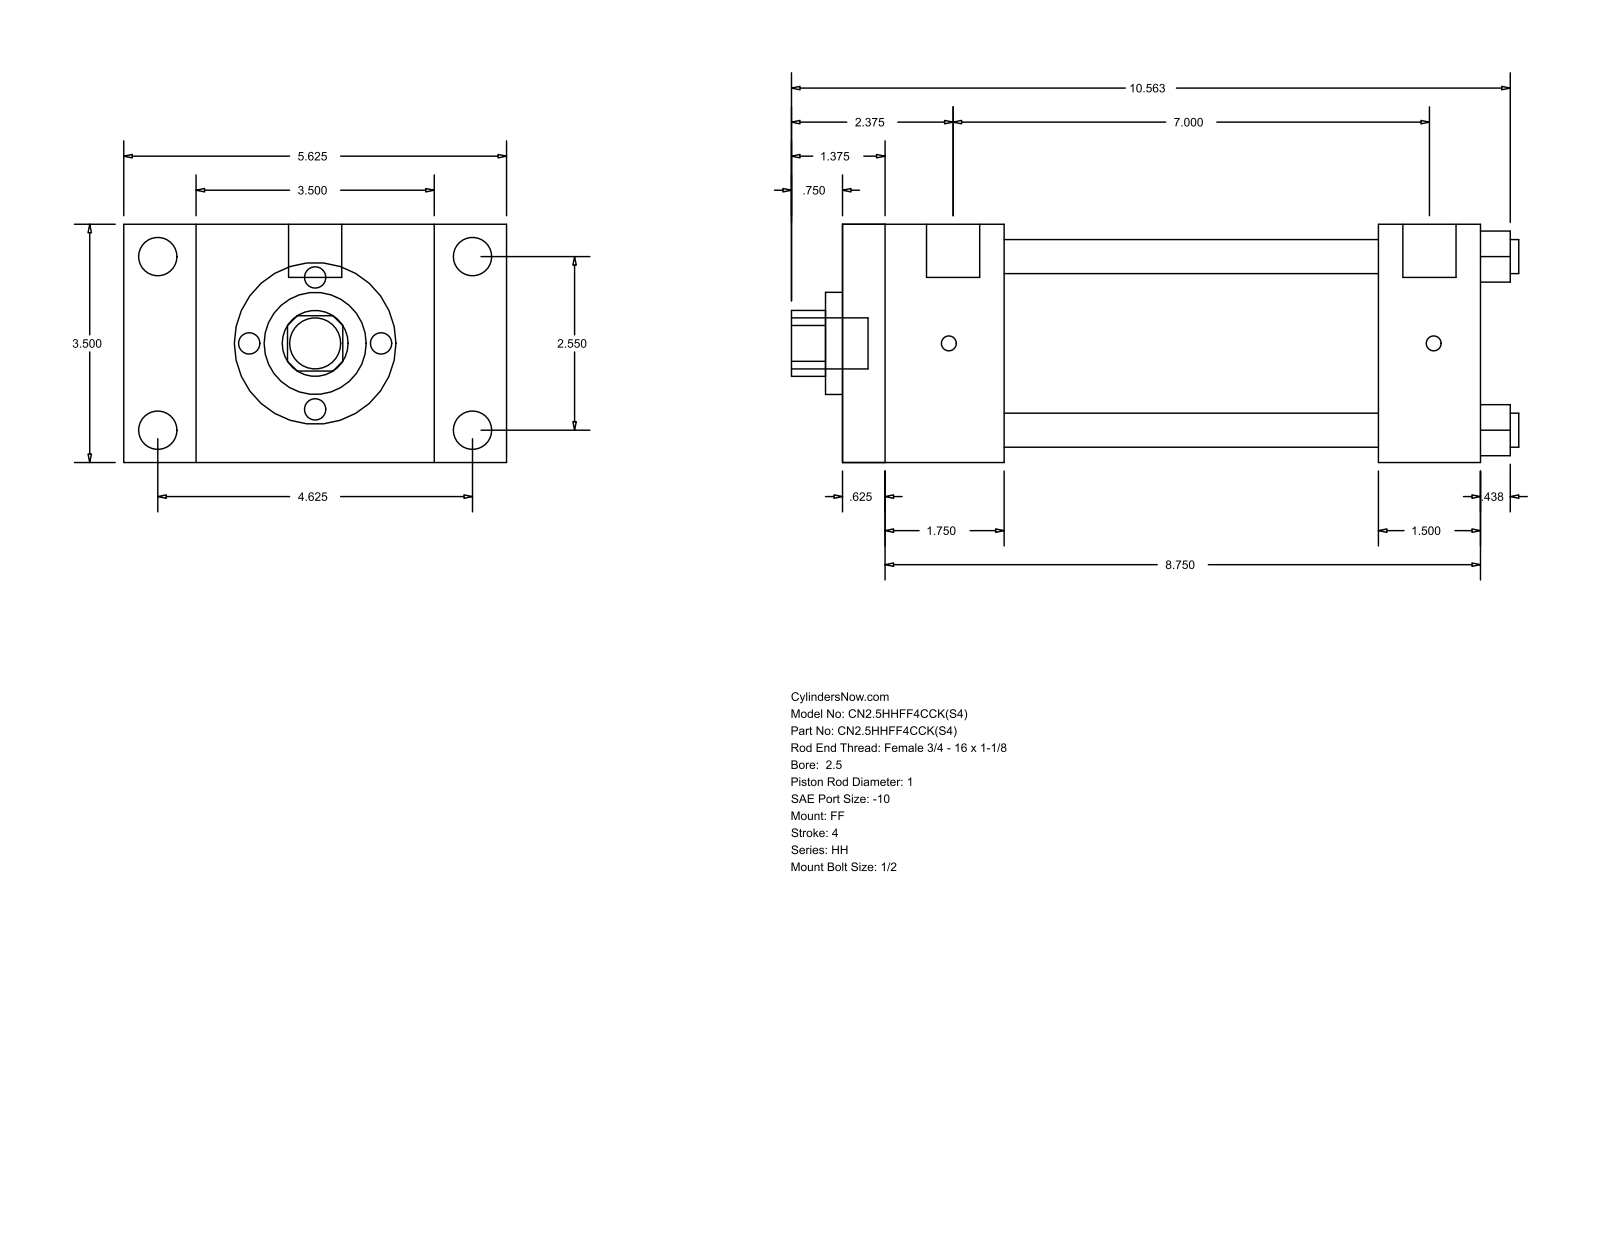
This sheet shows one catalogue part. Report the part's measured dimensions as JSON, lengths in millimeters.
{"part_name": "HH_FF__0250_1", "step_written_by": "GSSL Pune (CONFIG_CONTROL_DESIGN)", "units": "millimeters", "bodies": {"solids": 0, "faces": 92, "planar": 64, "cylindrical": 28, "other": 0}, "overall_size": [271.46, 142.88, 88.9], "round_holes": [[12.7, 4], [25.4, 1], [38.1, 1], [73.03, 1]], "round_bosses_or_shafts": [[14.3, 4], [5.56, 4], [19.84, 2], [19.05, 1]], "partial_cylinders_radius": [[12.29, 1]], "face_to_face_distances": [88.9, 238.13, 15.87, 222.26, 60.33, 44.46, 177.8, 200.02, 184.15, 139.69], "hole_center_spacings": [45.79, 64.76, 91.58]}
